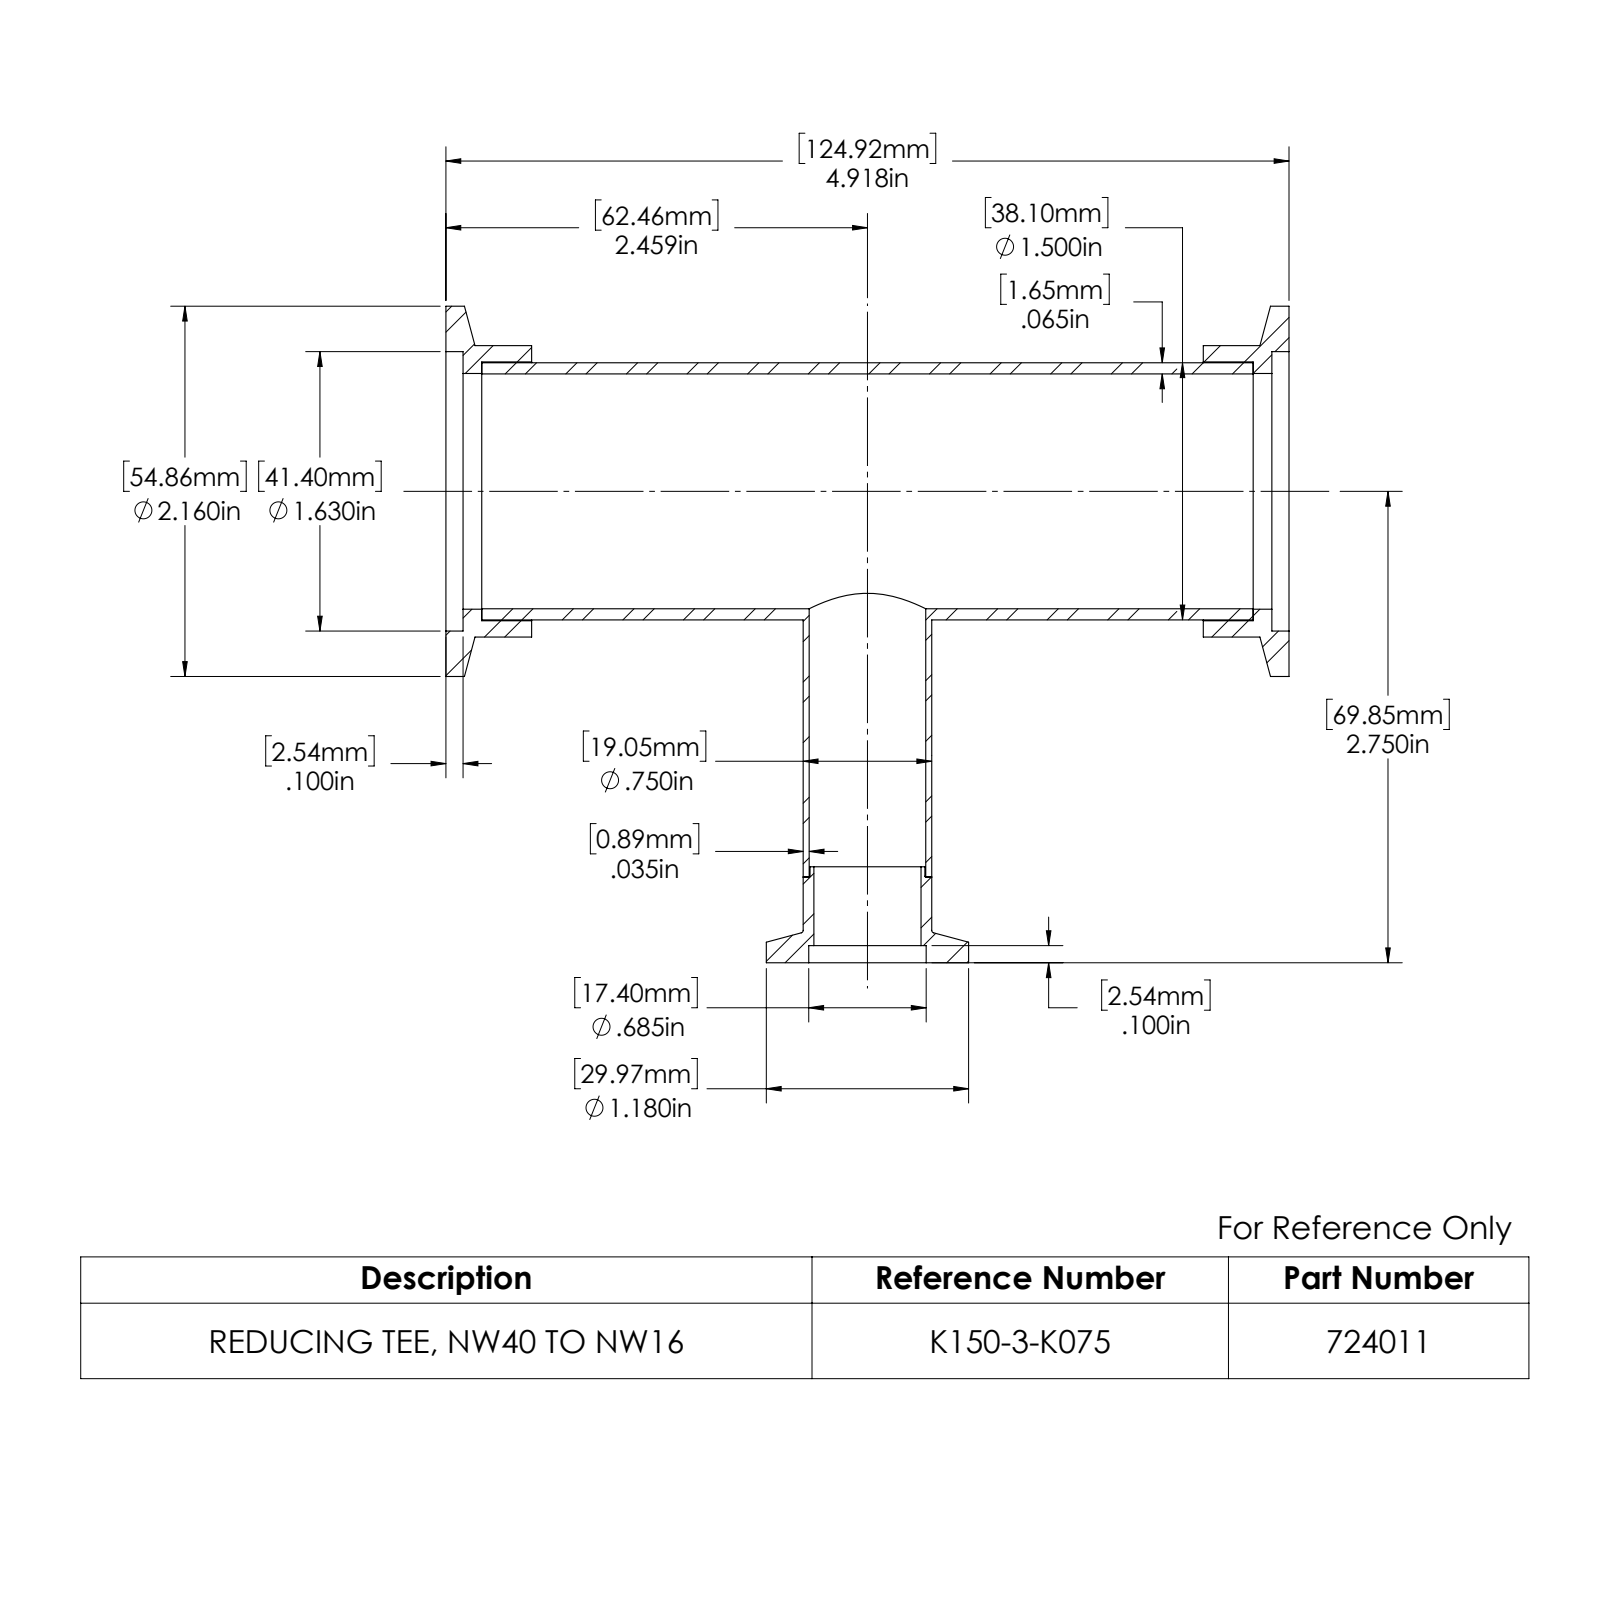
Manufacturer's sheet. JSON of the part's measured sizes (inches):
{"part_name": "724011; 713003-99; 713001; 404545", "step_written_by": "SolidWorks 2022 (AUTOMOTIVE_DESIGN)", "units": "inches", "bodies": {"solids": 4, "faces": 63, "planar": 15, "cylindrical": 38, "other": 10}, "overall_size": [4.918, 3.83, 2.16], "volume_in3": 2.446, "surface_area_in2": 70.07, "round_holes": [[0.625, 1], [0.68, 1], [0.685, 1], [1.37, 1], [1.375, 1], [1.51, 1], [1.63, 1]], "round_bosses_or_shafts": [[2.16, 1], [1.7, 1], [1.5, 1], [1.18, 1], [0.75, 1], [0.67, 1]], "face_to_face_distances": [4.918, 0.1, 4.818, 0.209, 4.709, 0.109, 4.609, 0.5, 0.4, 4.418]}
